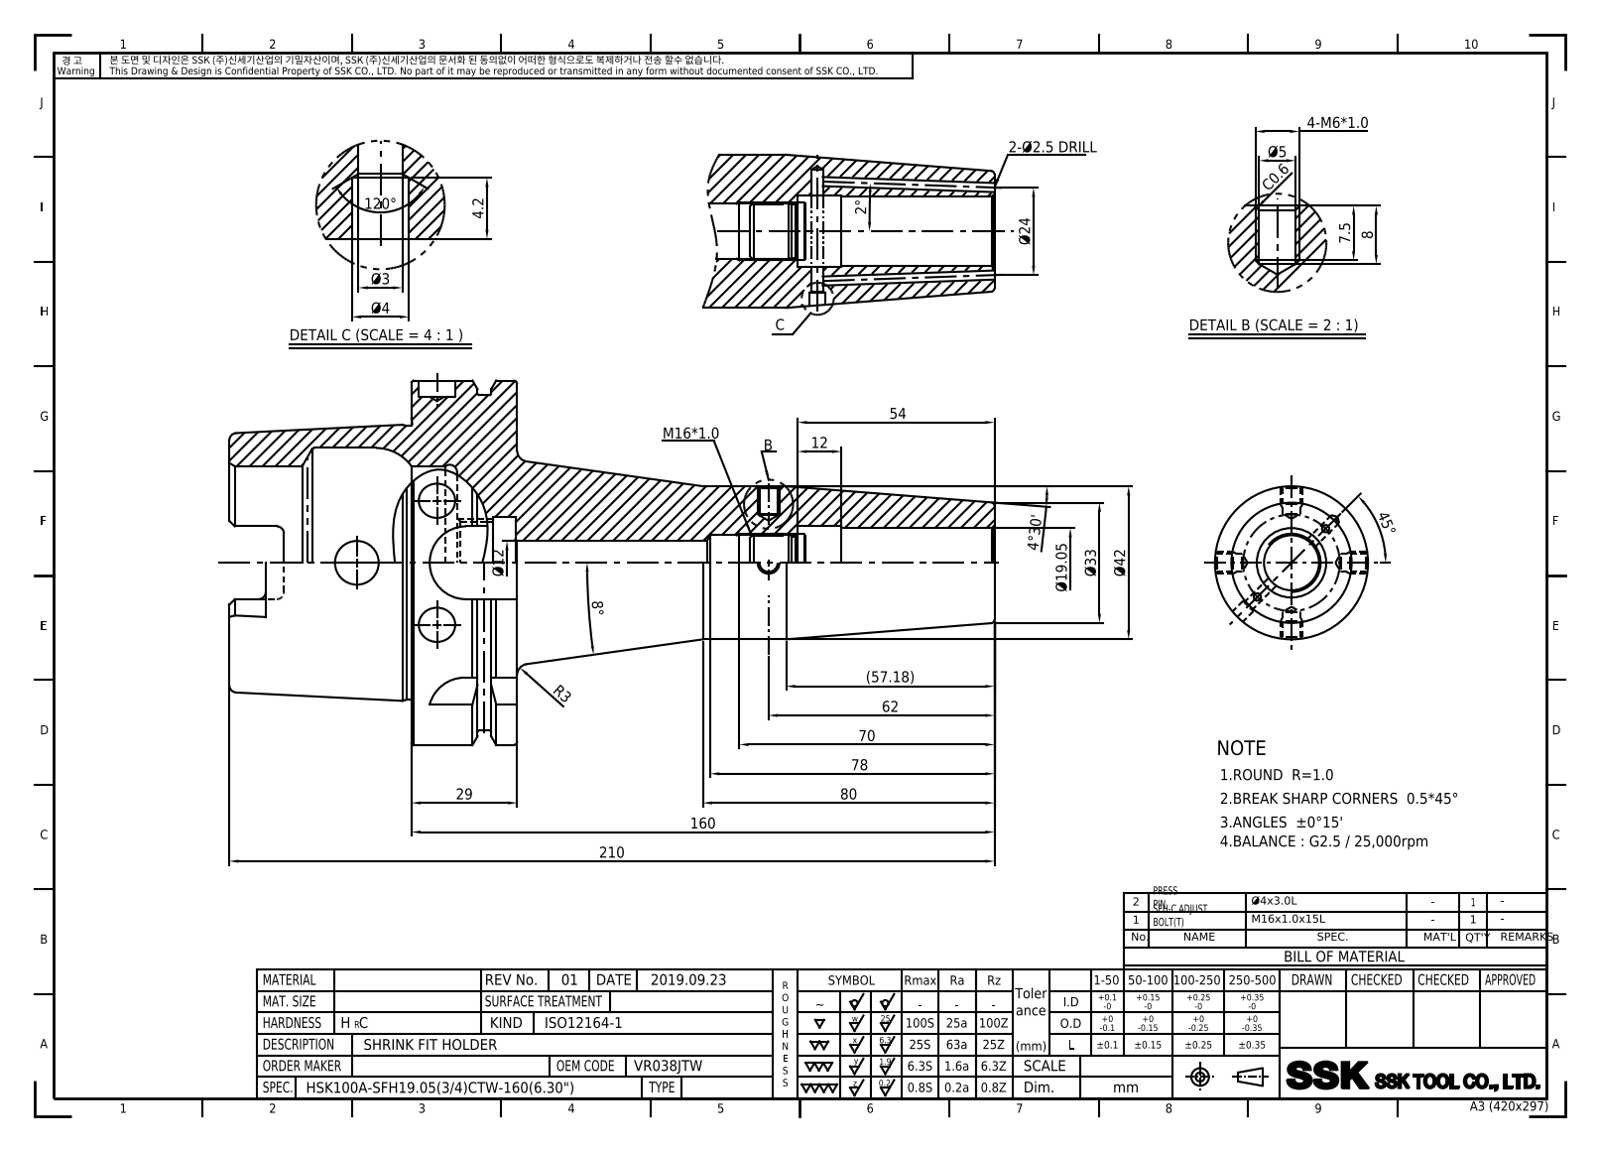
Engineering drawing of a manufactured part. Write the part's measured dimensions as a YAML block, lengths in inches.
part_name: "LO-HSK100A-SFH19.05CTW-160"
step_written_by: "Autodesk Inventor 2022 (AUTOMOTIVE_DESIGN)"
units: inches
bodies: {solids: 1, faces: 120, planar: 38, cylindrical: 37, other: 45}
overall_size: [8.268, 3.937, 3.937]
volume: 25.66
surface_area: 112.7
round_holes:
  - {diameter: 0.079, count: 2}
  - {diameter: 0.472, count: 2}
  - {diameter: 0.394, count: 1}
  - {diameter: 0.587, count: 1}
  - {diameter: 0.75, count: 1}
  - {diameter: 0.797, count: 1}
  - {diameter: 0.881, count: 1}
  - {diameter: 0.984, count: 1}
  - {diameter: 2.087, count: 1}
  - {diameter: 2.48, count: 1}
round_bosses_or_shafts:
  - {diameter: 3.937, count: 1}
  - {diameter: 3.622, count: 1}
  - {diameter: 2.969, count: 1}
  - {diameter: 1.654, count: 1}
partial_cylinders:
  - {radius: 0.079, count: 6}
  - {radius: 0.192, count: 4}
  - {radius: 0.394, count: 4}
face_to_face_distances: [1.142, 0.492, 0.65, 2.461, 1.969, 3.11, 8.268, 6.299, 5.807, 5.157]
